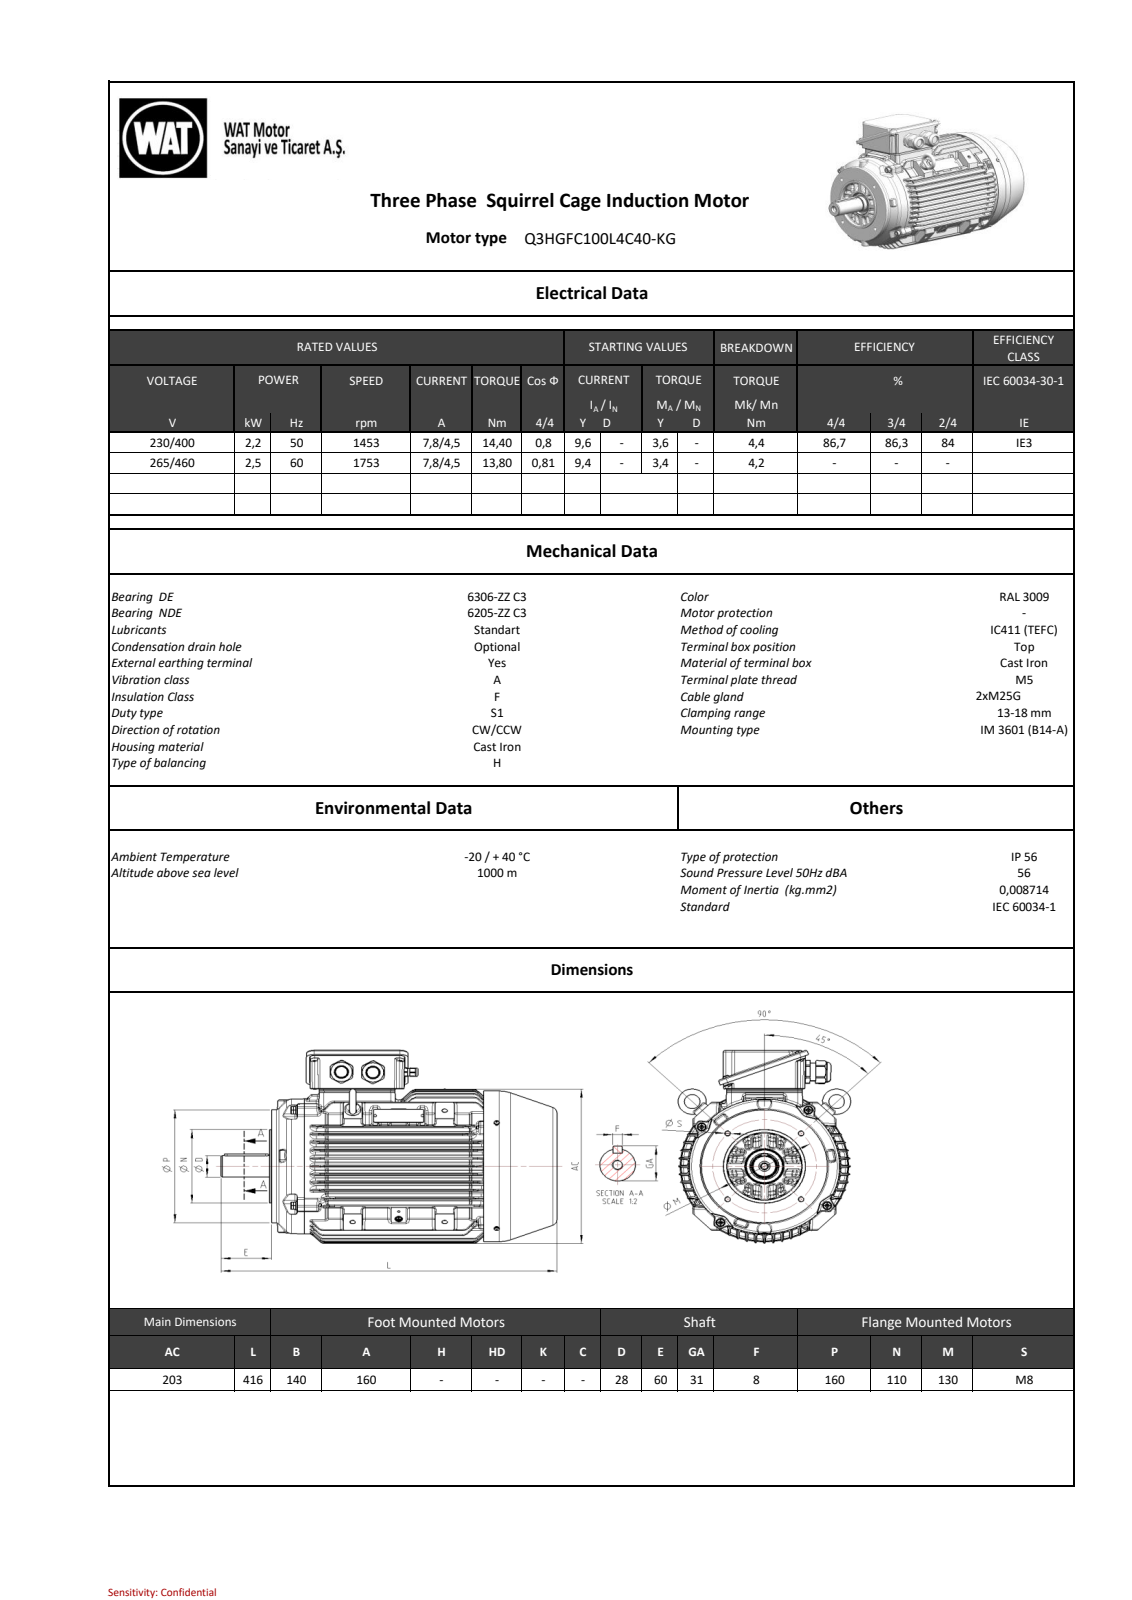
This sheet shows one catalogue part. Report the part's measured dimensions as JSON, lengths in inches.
{"part_name": "260051B46F5629tm", "step_written_by": "SIEMENS PLM Software NX 11.0 (AUTOMOTIVE_DESIGN)", "units": "inches", "bodies": {"solids": 0, "faces": 4281, "planar": 865, "cylindrical": 1069, "other": 2347}, "overall_size": [16.378, 10.746, 8.069], "round_holes": [[0.268, 10], [0.197, 8], [0.394, 5], [0.165, 2], [0.677, 2], [0.256, 1], [0.335, 1], [0.413, 1], [1.709, 1], [1.717, 1], [7.756, 1]], "round_bosses_or_shafts": [[0.472, 9], [0.394, 8], [0.341, 4], [0.315, 4], [0.157, 4], [1.091, 2], [0.994, 2], [0.787, 2]], "partial_cylinders_radius": [[0.157, 240], [0.059, 101], [0.118, 85], [0.071, 42], [0.039, 41], [0.079, 35], [0.01, 26], [1.043, 12]], "face_to_face_distances": [0.533, 1.069, 0.536, 1.608, 1.075, 0.539, 3.104, 2.028, 2.567, 2.035], "hole_center_spacings": [1.097, 3.524, 3.979, 4.7, 4.983, 6.06, 2.303, 2.815]}
